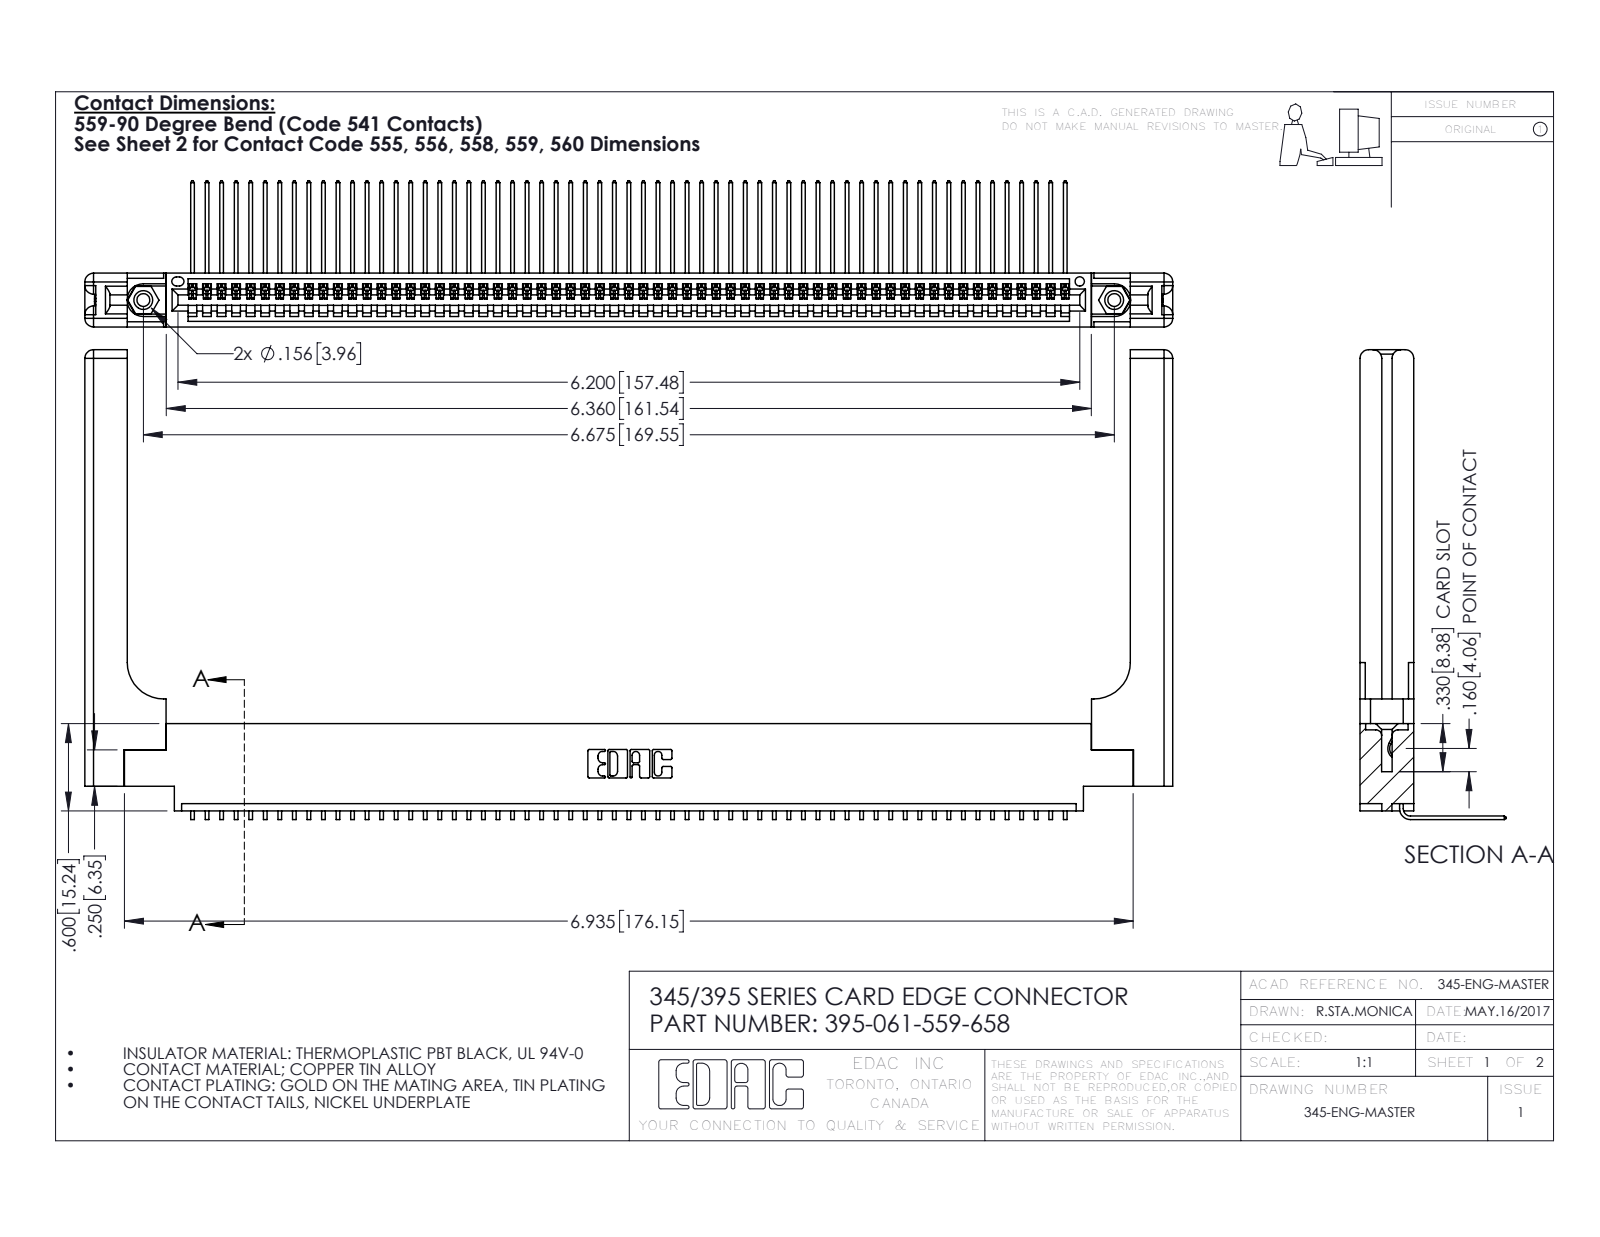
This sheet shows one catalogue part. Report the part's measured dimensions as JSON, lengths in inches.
{"part_name": "345-220-058_345-220-058; 395-061-559-658; 345-292-001_558 559 Tail - 1; 345-250-001_345-250-001-102 (+1 more)", "step_written_by": "SolidWorks 2016 (CONFIG_CONTROL_DESIGN)", "units": "inches", "bodies": {"solids": 66, "faces": 4046, "planar": 2794, "cylindrical": 1192, "other": 60}, "overall_size": [7.479, 3.229, 1.005], "volume_in3": 1.635, "surface_area_in2": 48.34, "round_holes": [[0.089, 2], [0.125, 2], [0.156, 2], [0.064, 1]], "round_bosses_or_shafts": [[0.155, 2]], "partial_cylinders_radius": [[0.006, 122], [0.01, 22], [0.06, 16], [0.007, 6], [0.031, 6], [0.026, 3], [0.03, 2], [0.031, 2]], "face_to_face_distances": [0.37, 0.072, 0.298, 0.098, 0.272, 0.025, 0.2, 0.225, 0.148, 0.15], "hole_center_spacings": [0.27, 6.439, 6.675]}
